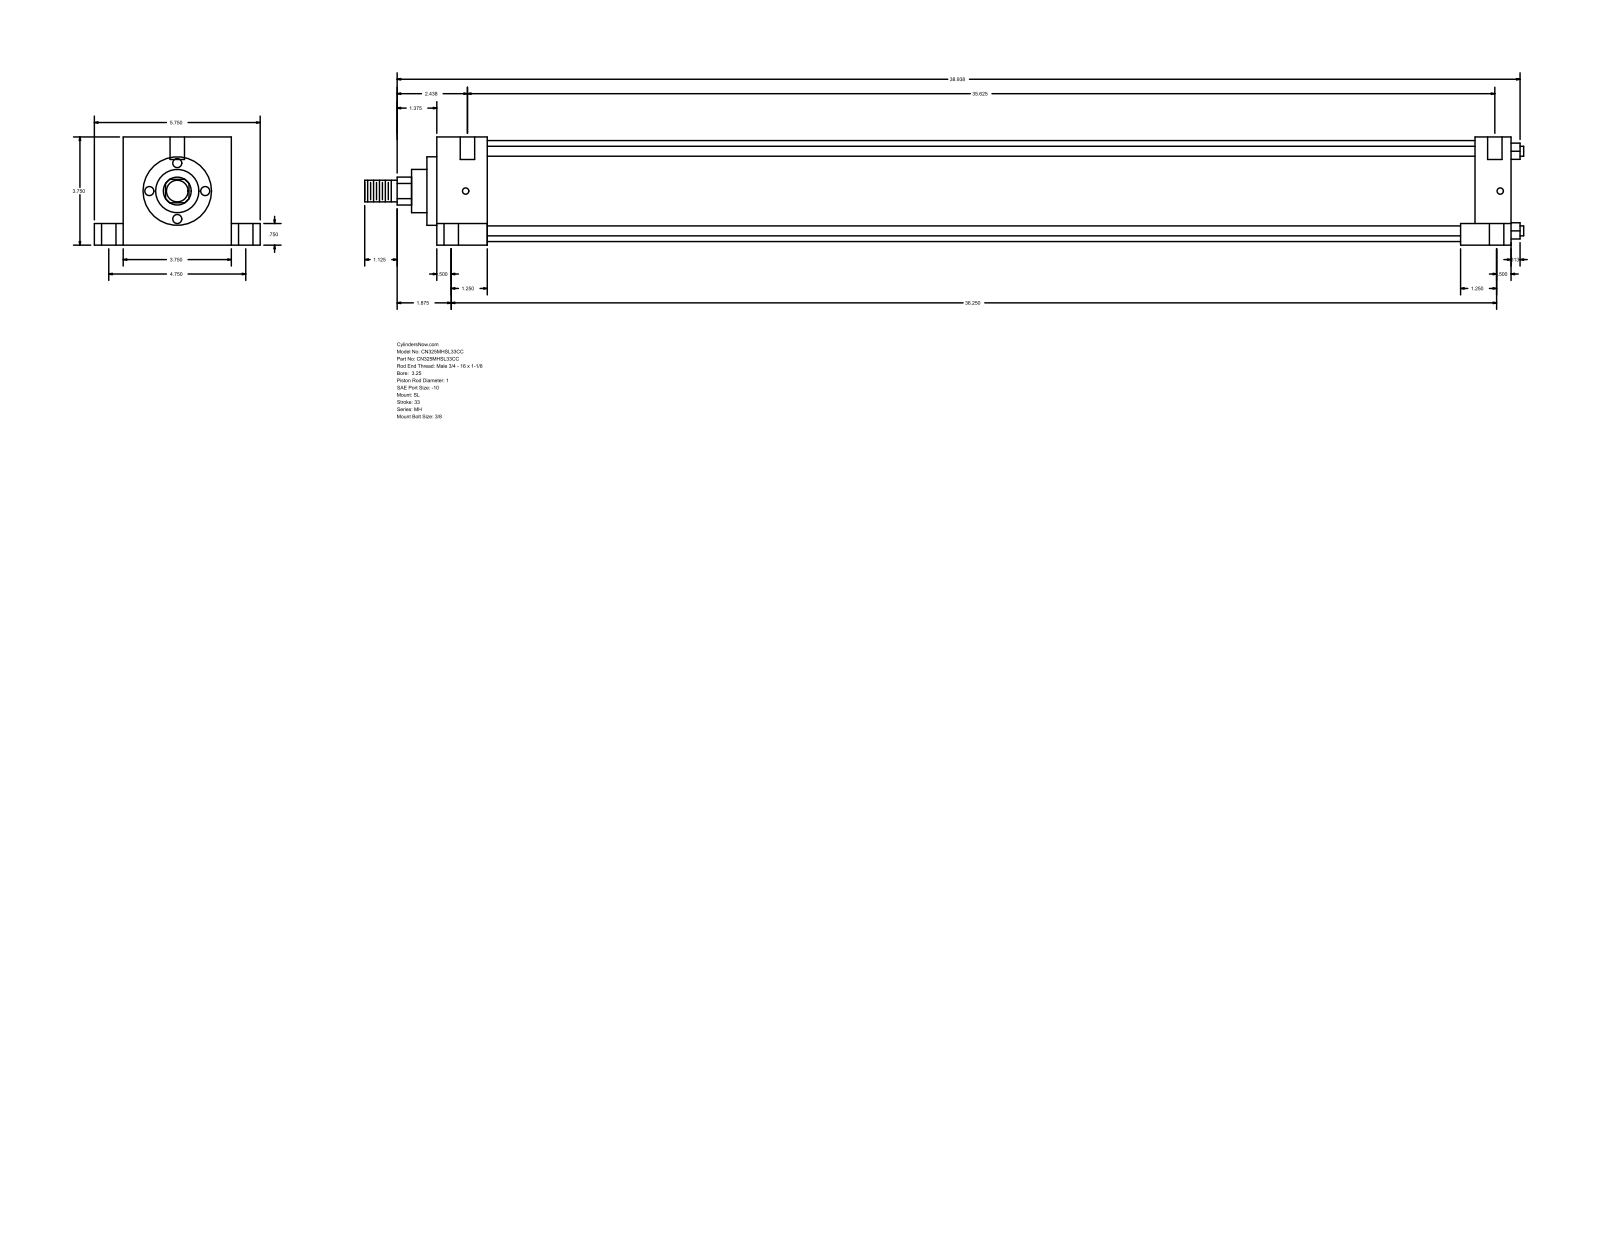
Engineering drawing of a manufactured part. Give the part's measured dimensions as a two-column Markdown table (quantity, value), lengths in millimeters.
| quantity | value |
| --- | --- |
| part name | MH_SL__0325_1 |
| STEP written by | GSSL Pune (CONFIG_CONTROL_DESIGN) |
| units | millimeters |
| bodies | 0 solids, 110 faces (77 planar, 33 cylindrical, 0 other) |
| overall size | 1020.76 × 146.05 × 95.25 |
| round holes (diameter × count) | 12.7 × 6, 5.56 × 4, 19.05 × 4 |
| round bosses / shafts (diameter × count) | 8.76 × 4, 88.9 × 1, 60.33 × 1, 38.1 × 1, 25.4 × 1, 19.05 × 1 |
| partial cylindrical surfaces (radius × count) | 12.29 × 1 |
| main face-to-face distances | 95.24, 946.16, 44.46, 901.7, 25.41, 120.65, 19.05, 76.19, 914.41, 869.95 |
| hole center spacings | 60.35, 60.41, 61.65, 62, 120.66, 908.48, 910.05, 911.22 |
